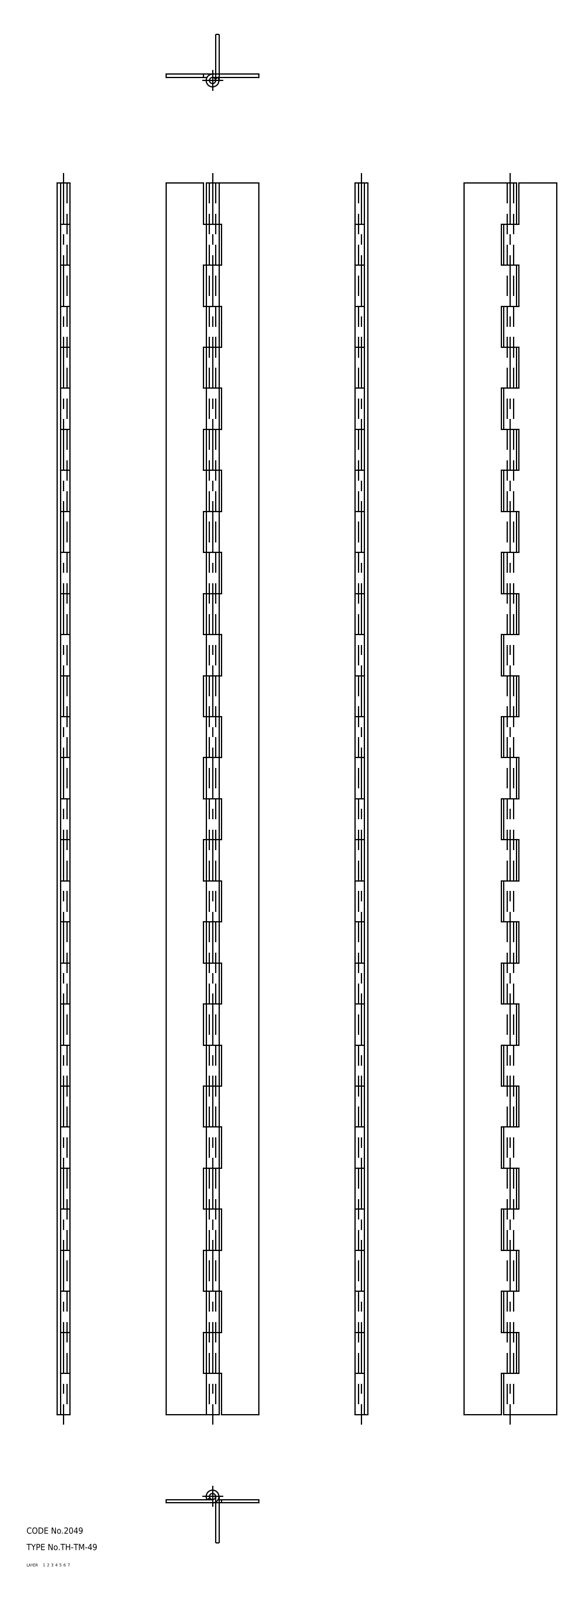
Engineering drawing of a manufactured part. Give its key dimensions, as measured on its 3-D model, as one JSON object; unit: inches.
{"part_name": "hinge piece_B; hinge piece_A; shaft; TH_TM_49_23767_36", "step_written_by": "CADfix (AUTOMOTIVE_DESIGN)", "units": "inches", "bodies": {"solids": 3, "faces": 192, "planar": 0, "cylindrical": 0, "other": 192}, "overall_size": [23.622, 1.772, 0.244], "volume_in3": 3.344, "surface_area_in2": 115.3}
